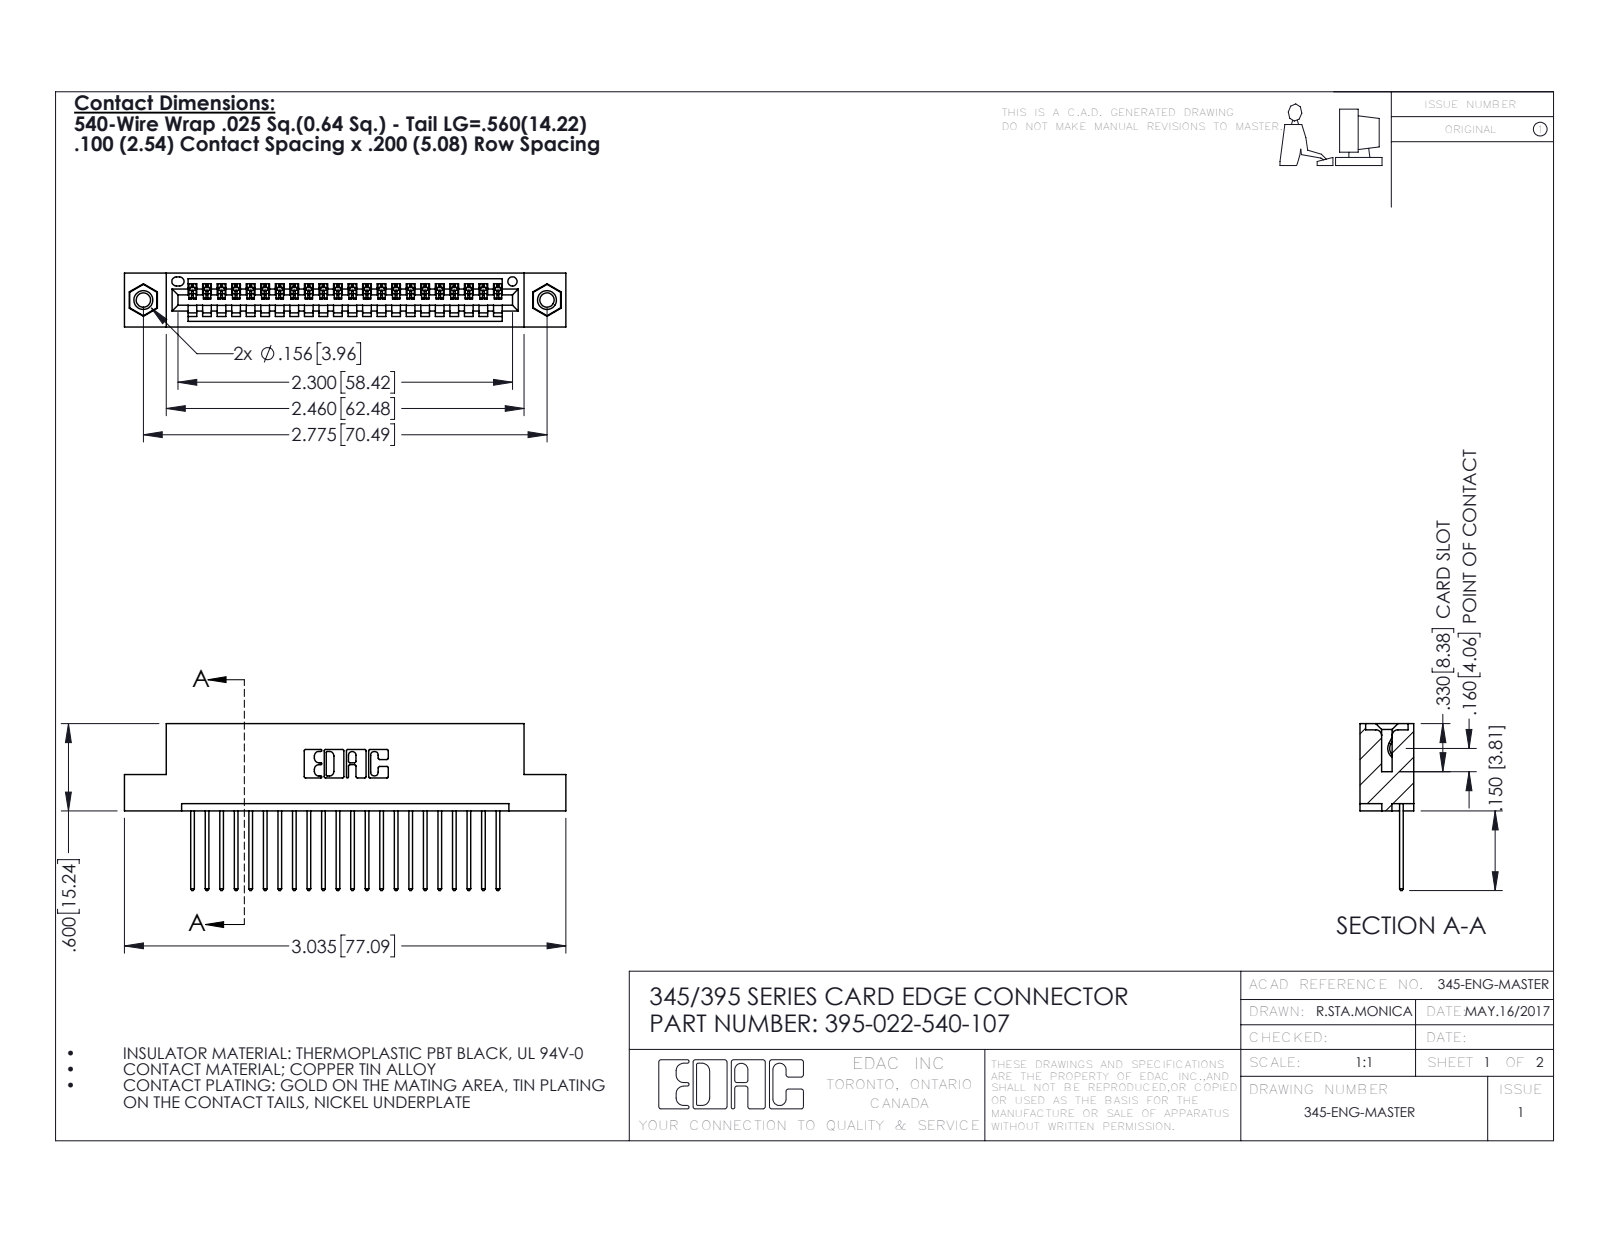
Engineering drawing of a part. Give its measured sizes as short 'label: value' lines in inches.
name: 395-022-540-107; 345-250-001_345-250-005-103; 345-292-001_345-293-140; 345 Part_Flush Mounting Lugs - 0.156 Dia-TI
written by: SolidWorks 2016 (CONFIG_CONTROL_DESIGN)
unit: in
bodies: 25 solids, 1462 faces (992 planar, 454 cylindrical, 16 other)
size: 3.035 × 1.147 × 0.37
volume: 0.438 in³; area: 14.74 in²
holes: 2× ⌀0.098, 2× ⌀0.125, 2× ⌀0.156, 1× ⌀0.064
bosses: 2× ⌀0.155
rounds: 44× R0.006, 44× R0.01, 22× R0.01, 6× R0.007, 6× R0.031, 3× R0.026, 2× R0.031, 2× R0.04
face distances: 0.072, 0.298, 0.2, 0.37, 0.098, 0.272, 0.025, 0.225, 0.149, 0.072
hole spacings: 0.27, 2.541, 2.775
